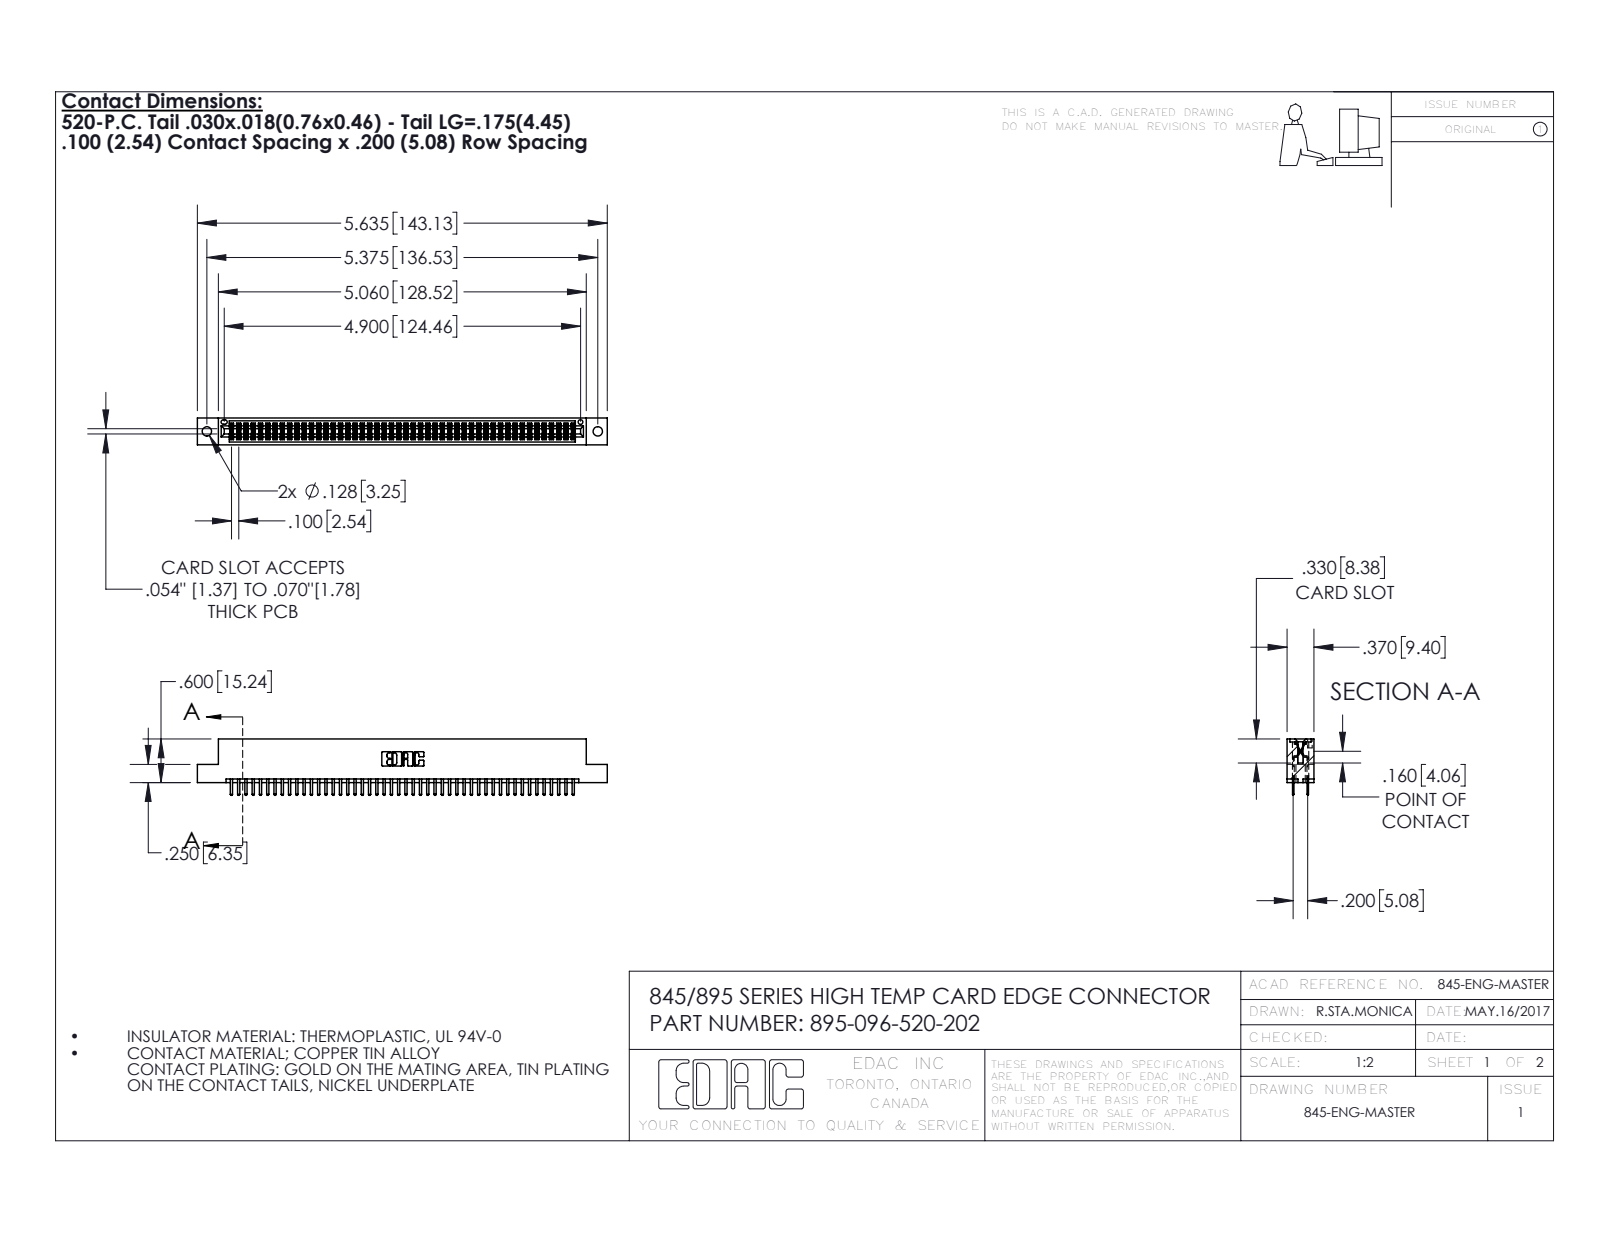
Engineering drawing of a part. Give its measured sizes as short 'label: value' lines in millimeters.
name: 345-292-001_345-293-120; 345 Part_Flush Mounting Lugs - 0.128 Dia; 395-096-520-202
written by: SolidWorks 2016 (CONFIG_CONTROL_DESIGN)
unit: mm
bodies: 97 solids, 5310 faces (3440 planar, 1870 cylindrical, 0 other)
size: 143.1 × 19.7 × 9.4
volume: 13 900 mm³; area: 20 270 mm²
holes: 2× ⌀3.3, 1× ⌀1.6
rounds: 144× R0.2, 100× R0.3, 22× R0.3, 6× R0.2, 6× R0.8, 3× R0.7, 2× R0.4, 2× R0.5
face distances: 7.6, 1.8, 5.1, 9.4, 2.5, 6.9, 0.6, 5.7, 0.6, 1.8
hole spacings: 6.9, 130.5, 136.5
